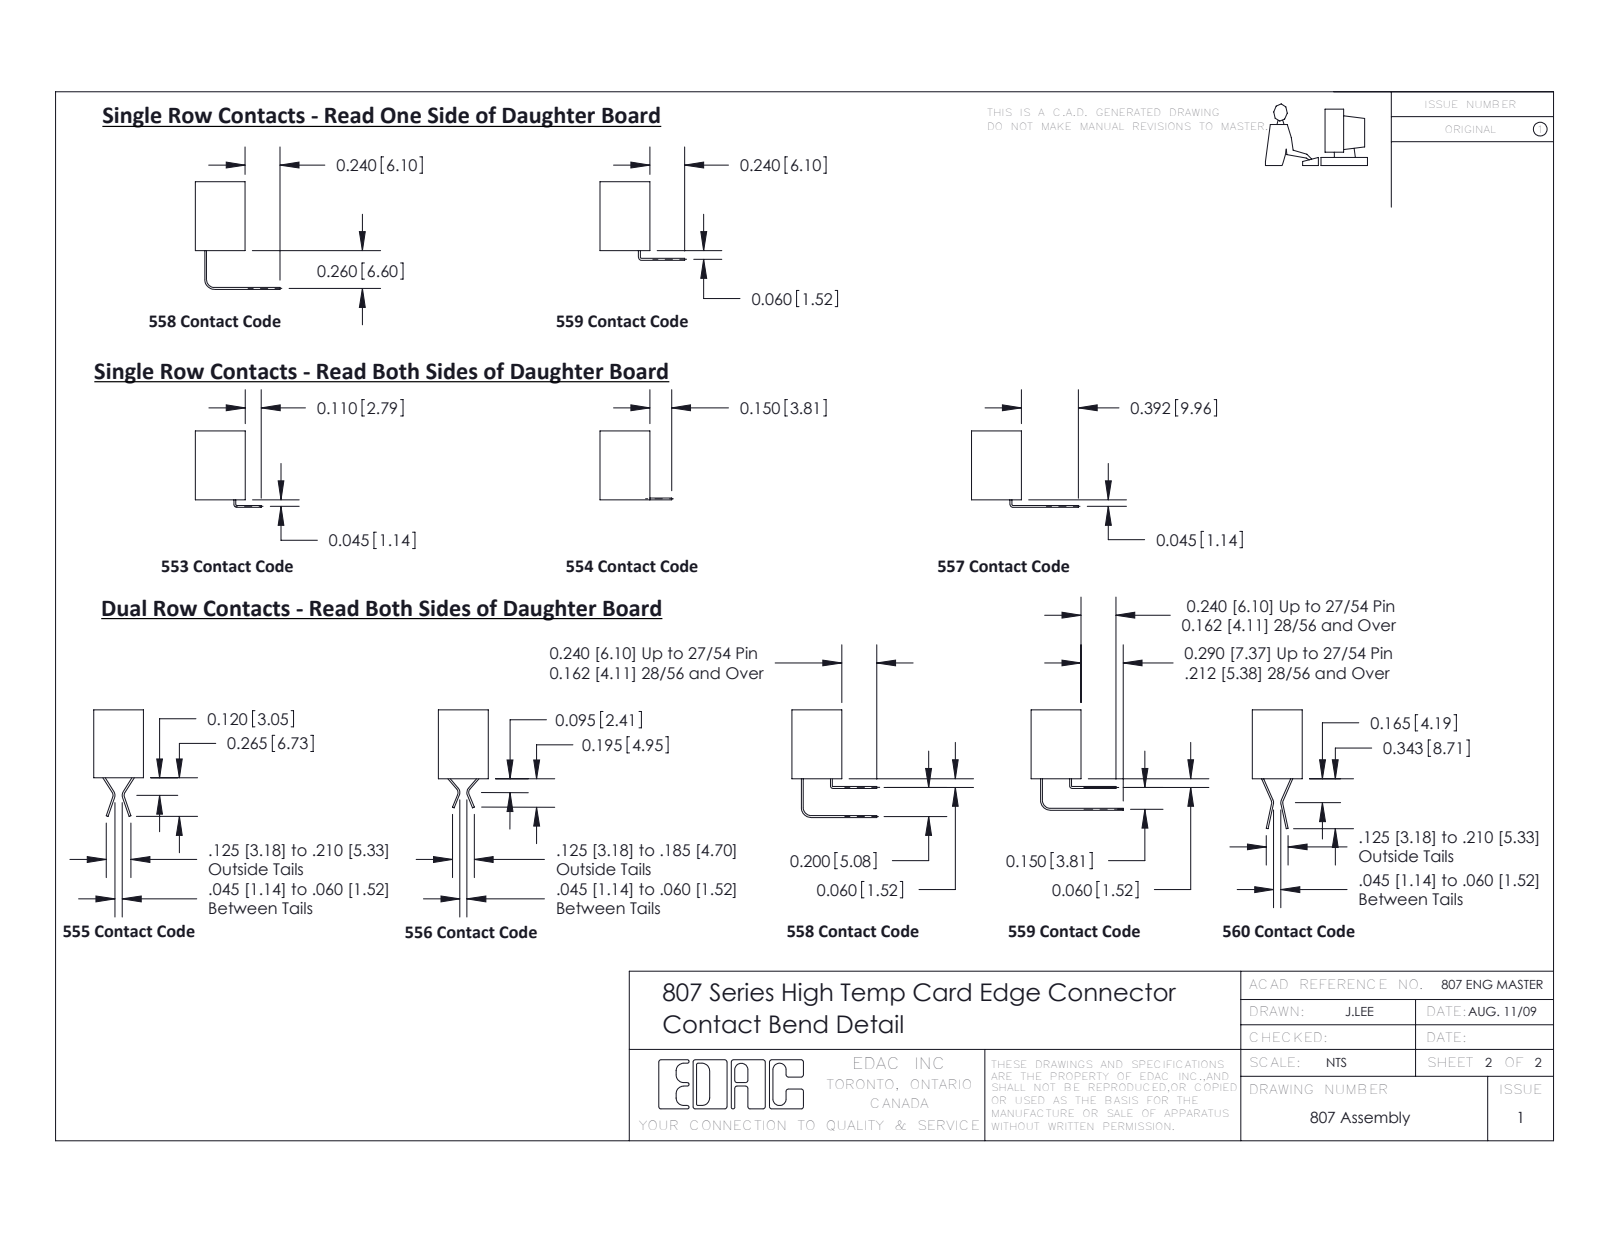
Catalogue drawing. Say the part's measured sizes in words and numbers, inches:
The part is named "307-290-002_521; 307 Part_.156 Dia Mounting Holes; 345-250-001_345-250-003-102; 357-011-521-108". Its 3-D file was written by "SolidWorks 2016 (CONFIG_CONTROL_DESIGN)". It is 14 solids with 1004 faces: 597 planar, 367 cylindrical and 40 other. Overall it measures 2.622 by 0.686 by 0.343 inches. Its volume is 0.268 cubic inches and its surface area 11.45 square inches. Round holes: 2 of diameter 0.089, 2 of diameter 0.125, 2 of diameter 0.156. Round bosses or shafts: 2 of diameter 0.155. Partial cylindrical surfaces (rounded edges, fillets, slot ends): 38 of radius 0.02, 22 of radius 0.01, 11 of radius 0.023, 6 of radius 0.007, 6 of radius 0.031, 3 of radius 0.026, 2 of radius 0.012, 2 of radius 0.025. The main face-to-face distances are 0.013, 0.064, 0.343, 0.279, 0.202, 0.279, 0.215, 0.064, 0.077, 0.076. The hole center spacings are 2.312.
